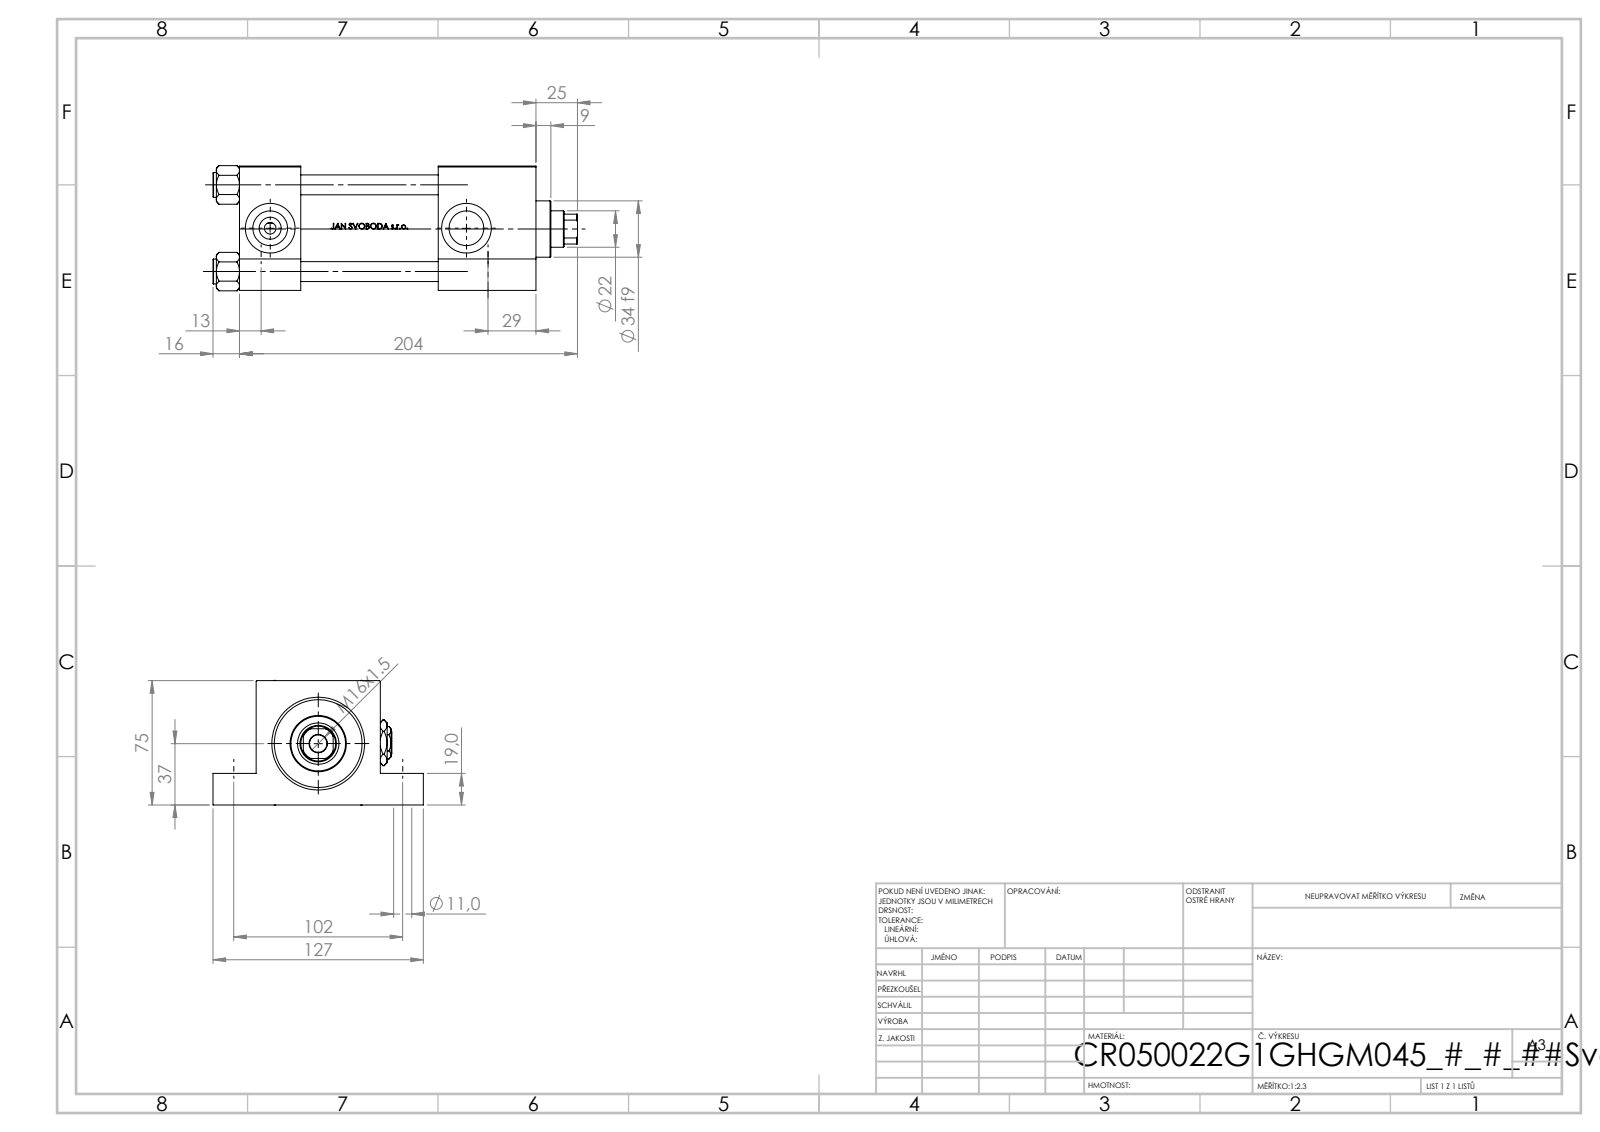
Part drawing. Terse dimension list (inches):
name: V215CR_G_Body; V215_VC_A; V215CR_VCP_G; V215CR_G_TYCINKA (+2 more)
written by: SolidWorks 2019 (CONFIG_CONTROL_DESIGN)
unit: in
bodies: 12 solids, 1134 faces (454 planar, 128 cylindrical, 552 other)
size: 8.661 × 5 × 2.974
volume: 47.95 in³; area: 271.4 in²
holes: 4× ⌀0.433, 4× ⌀0.472, 2× ⌀0.276, 2× ⌀0.825, 2× ⌀1.181, 1× ⌀0.413, 1× ⌀0.866, 1× ⌀0.984, 1× ⌀1.614, 1× ⌀1.969, 1× ⌀2.087
bosses: 4× ⌀0.591, 1× ⌀2.205, 1× ⌀1.339
rounds: 1× R0.413
face distances: 2.953, 1.457, 7.047, 5.591, 0.748, 2.205, 4.724, 3.268, 2.323, 1.024
hole spacings: 2.059, 1.442, 1.47, 2.912, 4.016, 5.394, 6.724, 4.665
